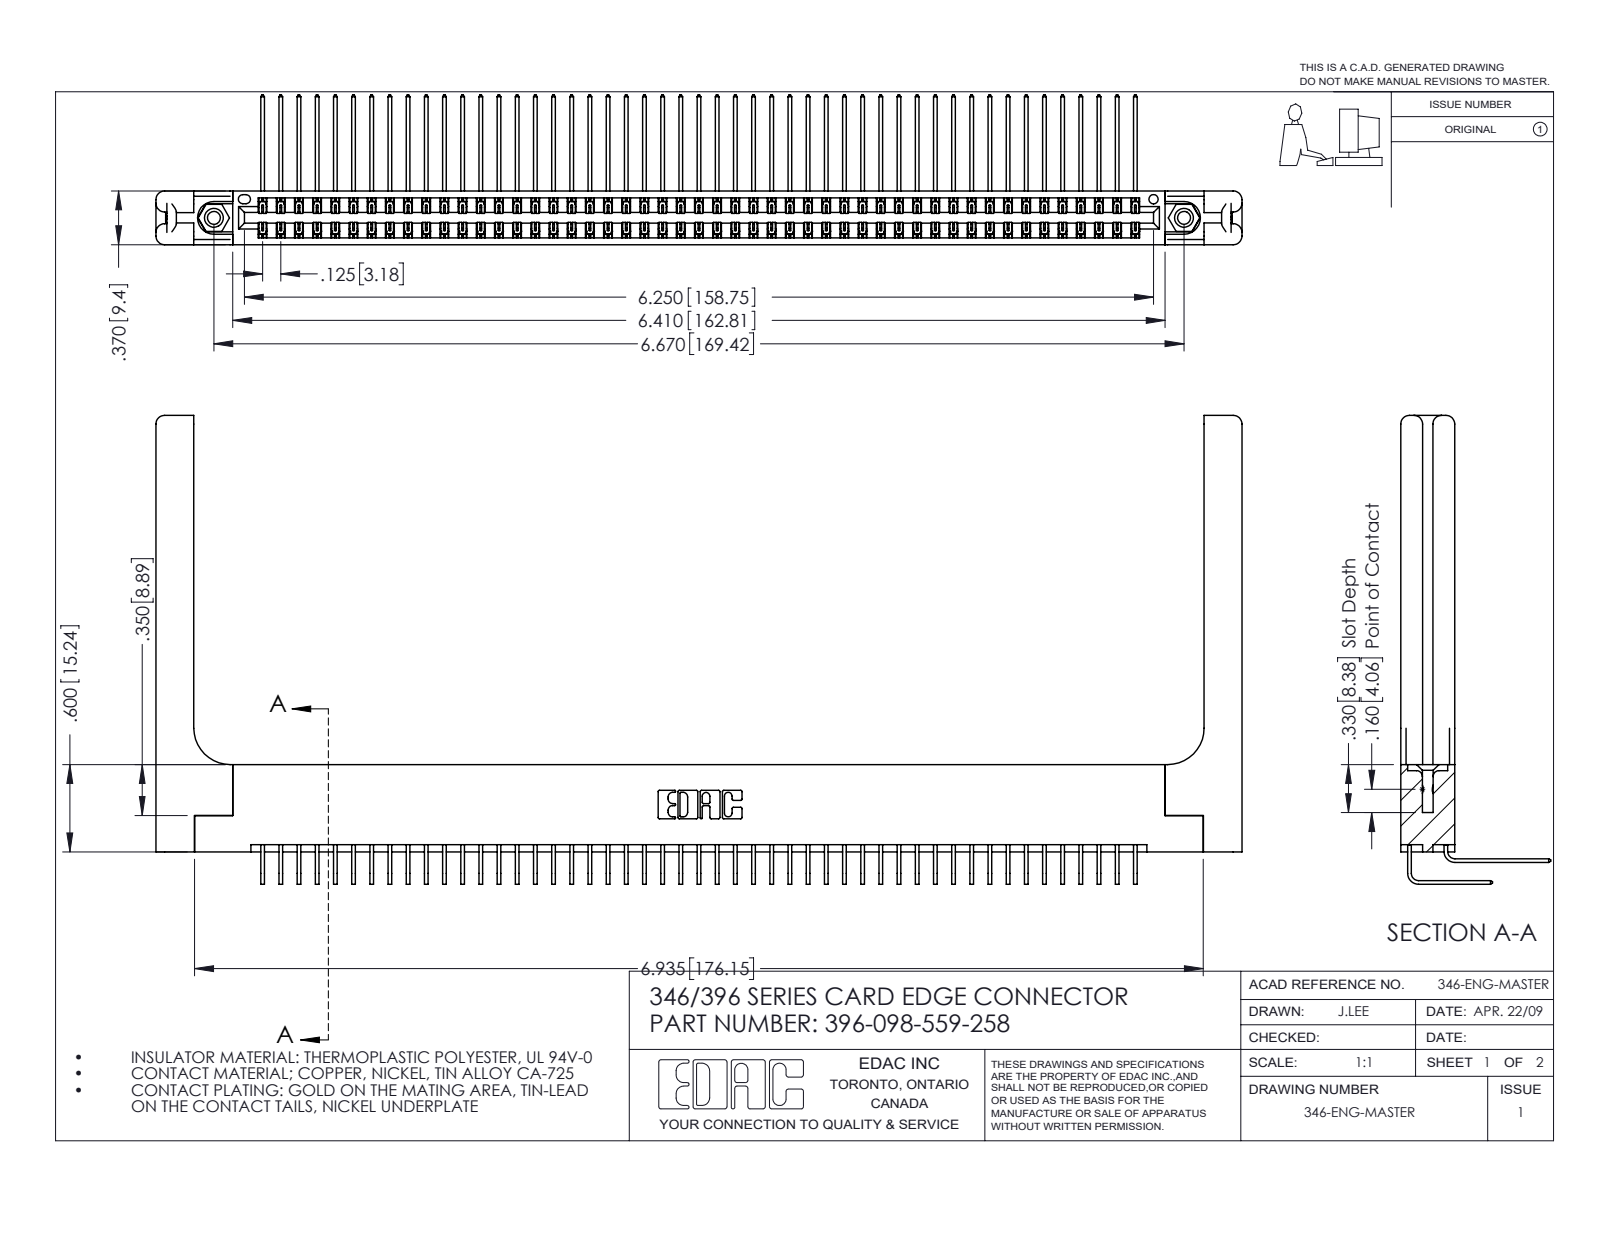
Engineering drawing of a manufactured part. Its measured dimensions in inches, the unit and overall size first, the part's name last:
Units: inches
Overall size (bounding box): 7.466 × 3.223 × 1.03
Round holes (diameter × count): ⌀0.089 ×2, ⌀0.125 ×2, ⌀0.156 ×2, ⌀0.064 ×1
Round bosses / shafts (diameter × count): ⌀0.155 ×2
Partial cylindrical surfaces — rounded edges, fillets, slot ends (radius × count): R0.006 ×147, R0.01 ×22, R0.06 ×16, R0.007 ×6, R0.031 ×6, R0.026 ×3, R0.014 ×2, R0.022 ×2
Main face-to-face distances: 0.048, 0.322, 0.37, 0.072, 0.025, 0.25, 0.148, 0.15, 0.298, 0.275
Hole centre spacings: 0.246, 6.461, 6.67
Volume: 1.624 in³ · Surface area: 52.8 in²
Bodies: 103 solids, 5670 faces (3850 planar, 1760 cylindrical, 60 other)
Part name (STEP PRODUCT): 396-098-559-258; 346-220-058_345-220-058; 345-250-001_345-250-001-102; 345-292-001_559 Tail - 2 (+2 more)
STEP written by: SolidWorks 2016 (CONFIG_CONTROL_DESIGN)
